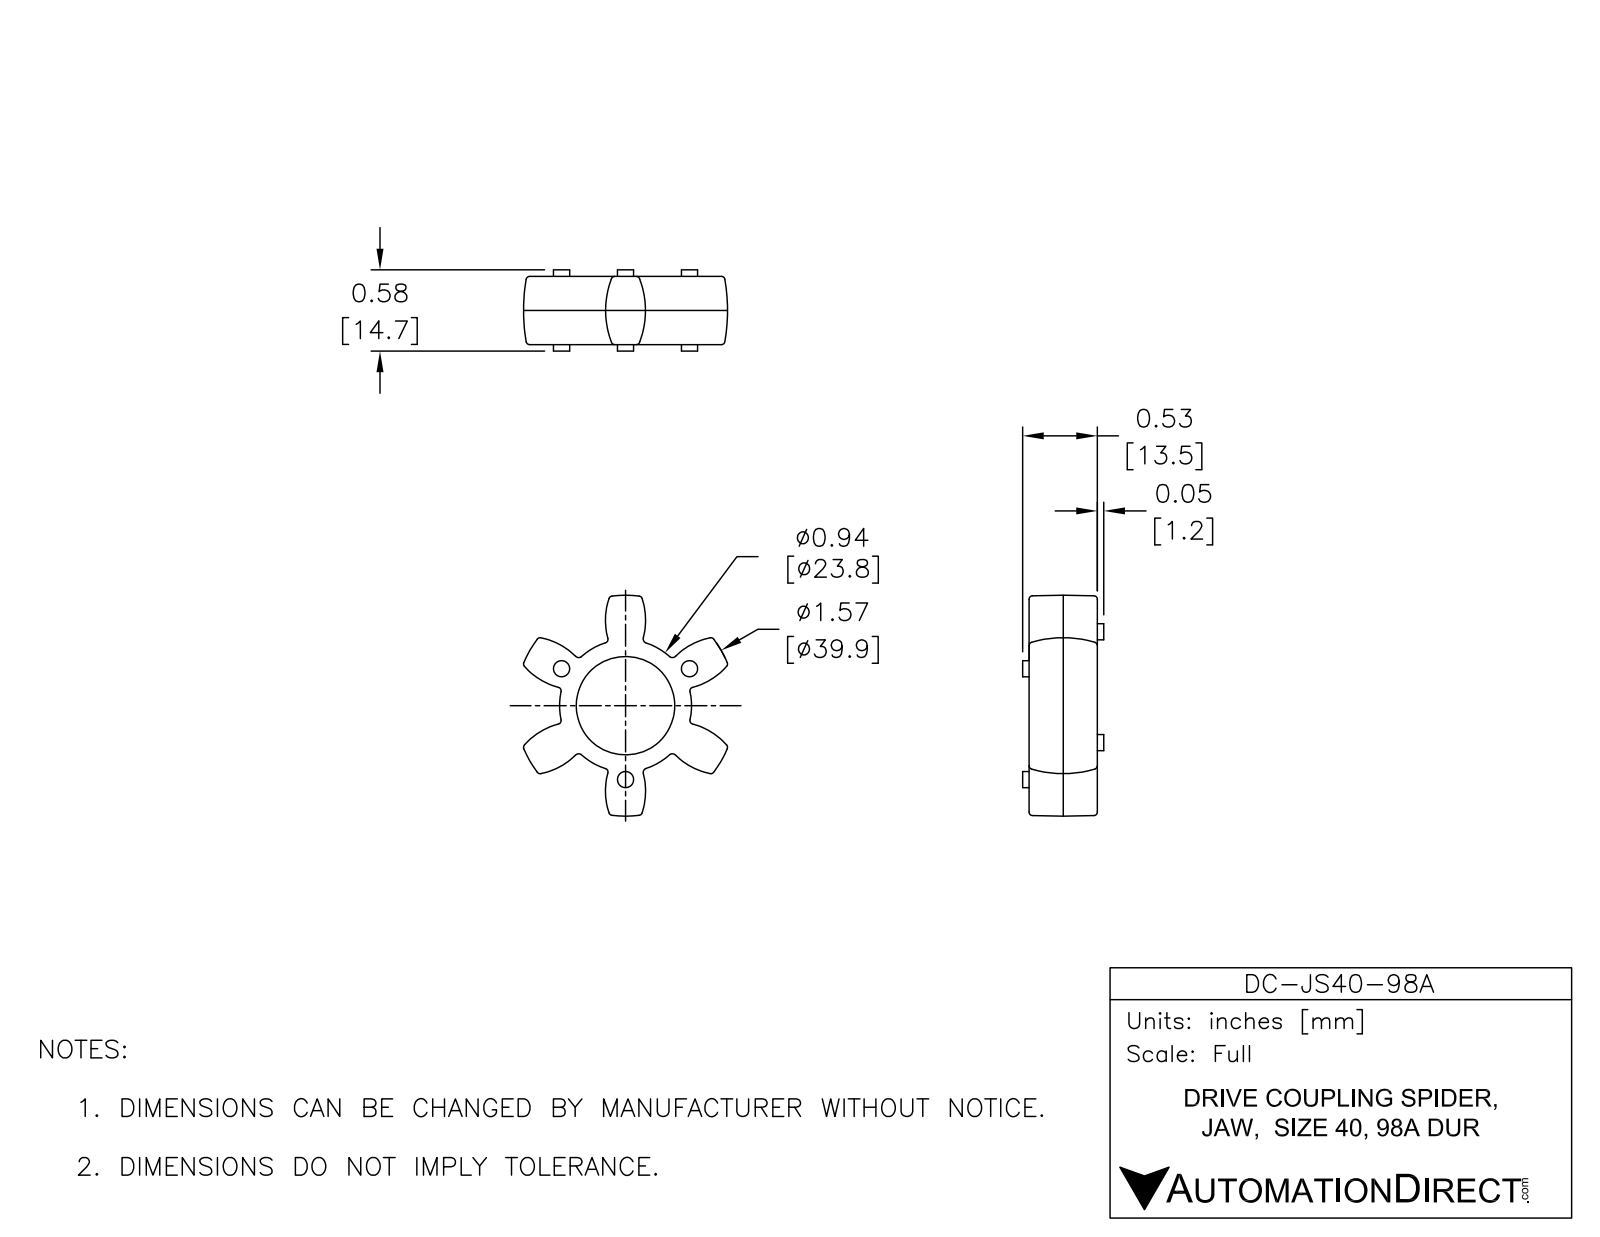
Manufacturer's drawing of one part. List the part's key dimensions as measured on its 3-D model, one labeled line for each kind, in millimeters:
Part name (STEP PRODUCT): DC-JS40-98A
STEP written by: SolidWorks 2015 (AUTOMOTIVE_DESIGN)
Units: millimetres
Bodies: 1 solid, 218 faces (8 planar, 14 cylindrical, 196 other)
Overall size (bounding box): 39.88 × 36.86 × 14.66
Volume: 6 394 mm³ · Surface area: 3 734 mm²
Round holes (diameter × count): ⌀17.78 ×1
Round bosses / shafts (diameter × count): ⌀2.92 ×6
Main face-to-face distances: 12.32, 1.17, 13.49, 14.66
